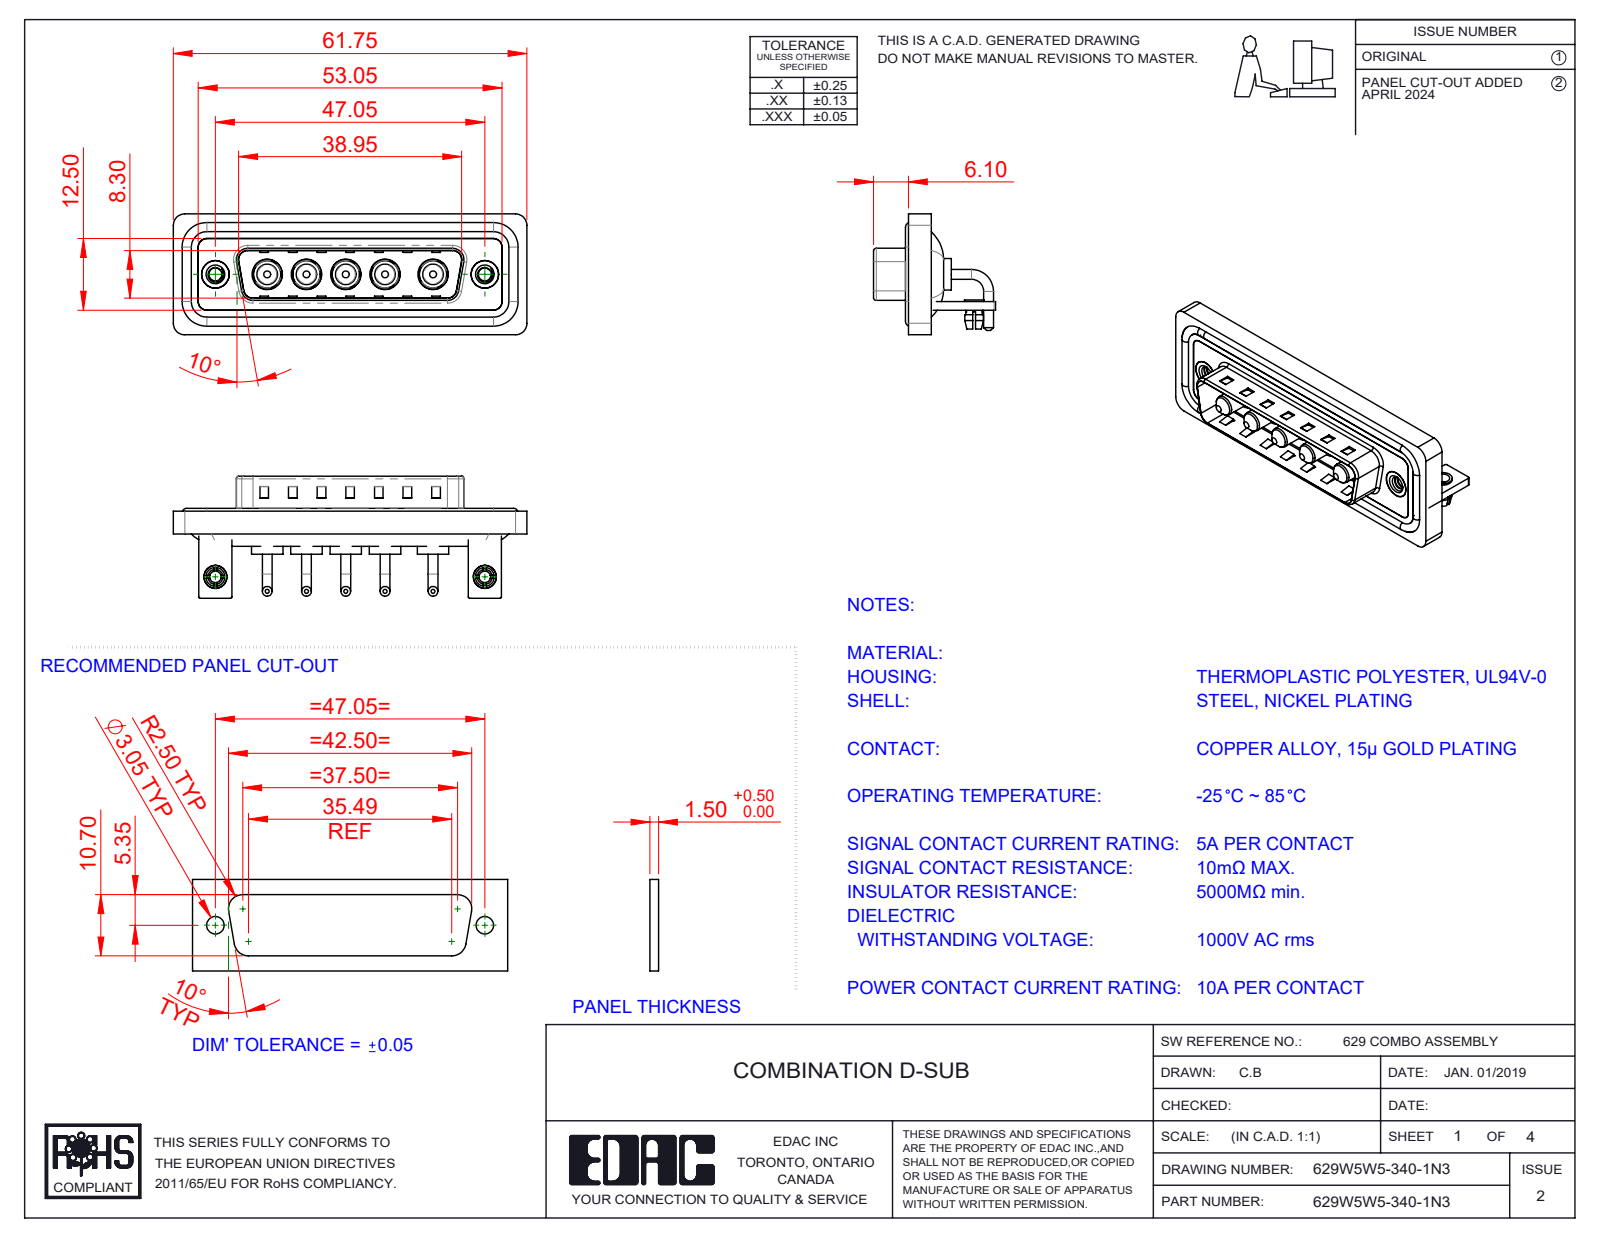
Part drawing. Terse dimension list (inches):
name: 629Combo Board Lock; 629W5W5-340-1N3; 629Combo Stabilizer Bracket; 629Combo Threaded Rivet_3 (+5 more)
written by: SolidWorks 2023 (CONFIG_CONTROL_DESIGN)
unit: in
bodies: 21 solids, 830 faces (327 planar, 343 cylindrical, 160 other)
size: 2.431 × 0.839 × 0.831
volume: 0.478 in³; area: 19.86 in²
holes: 5× ⌀0.191, 5× ⌀0.209, 2× ⌀0.079, 2× ⌀0.089, 2× ⌀0.098, 2× ⌀0.126, 2× ⌀0.157, 2× ⌀0.189, 2× ⌀0.197
bosses: 10× ⌀0.067, 5× ⌀0.217, 5× ⌀0.205, 5× ⌀0.187, 5× ⌀0.148, 5× ⌀0.142, 4× ⌀0.063, 2× ⌀0.193
rounds: 19× R0.079, 18× R0.059, 16× R0.01, 9× R0.02, 8× R0.063, 5× R0.083, 4× R0.024, 4× R0.026
face distances: 0.016, 0.059, 0.114, 0.031, 0.083, 0.043, 0.146, 0.177, 0.161, 0.047
hole spacings: 0.27, 0.541, 1.852, 0.27, 0.27, 0.33, 0.33, 0.356
